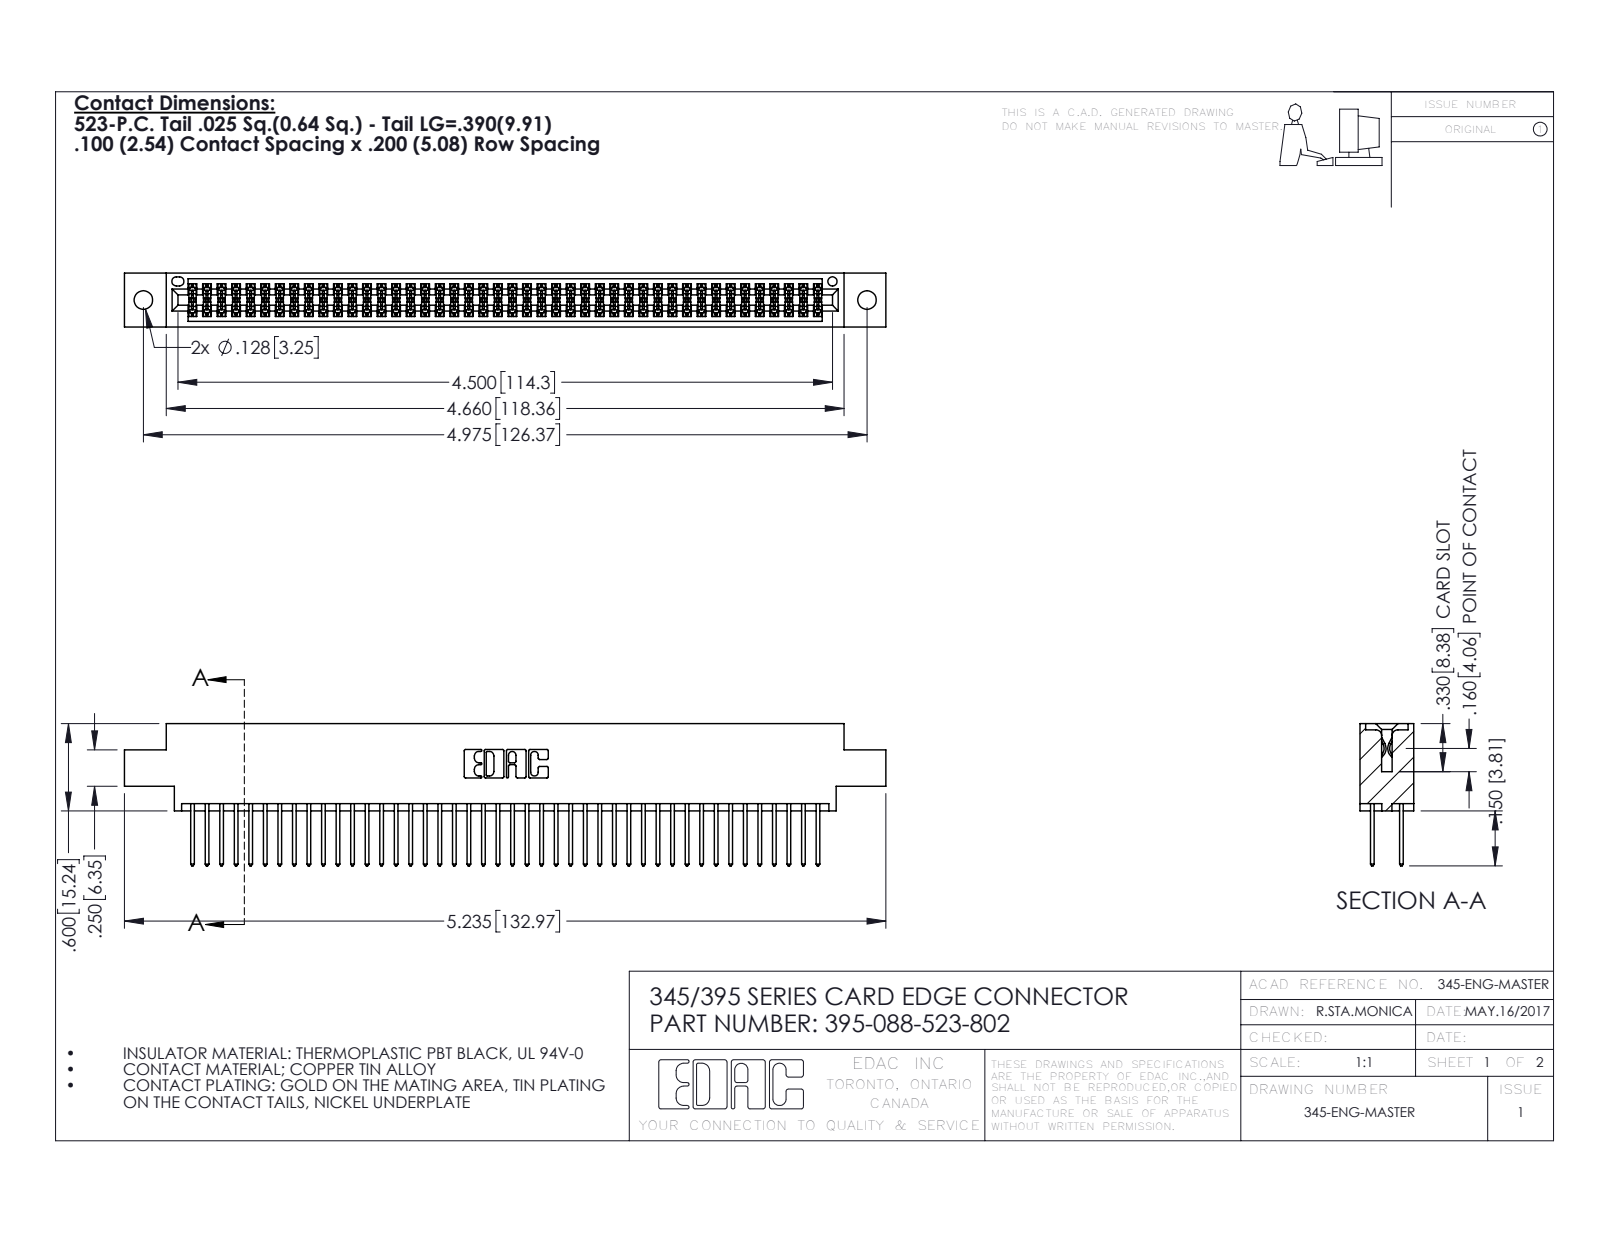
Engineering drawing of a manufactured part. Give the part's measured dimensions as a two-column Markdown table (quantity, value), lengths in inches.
| quantity | value |
| --- | --- |
| part name | 345-292-001_345-293-123; 395-088-523-802; 345 Part_0.170 Offset - 0.128 Dia |
| STEP written by | SolidWorks 2016 (CONFIG_CONTROL_DESIGN) |
| units | inches |
| bodies | 89 solids, 4530 faces (2988 planar, 1542 cylindrical, 0 other) |
| overall size | 5.235 × 0.977 × 0.37 |
| volume | 0.791 in³ |
| surface area | 30.82 in² |
| round holes (diameter × count) | 0.128 × 2, 0.064 × 1 |
| partial cylindrical surfaces (radius × count) | 0.006 × 132, 0.01 × 88, 0.01 × 22, 0.007 × 6, 0.031 × 6, 0.026 × 3, 0.014 × 2, 0.019 × 2 |
| main face-to-face distances | 0.298, 0.072, 0.2, 0.098, 0.272, 0.025, 0.37, 0.225, 0.175, 0.149 |
| hole center spacings | 0.27, 4.739, 4.975 |
